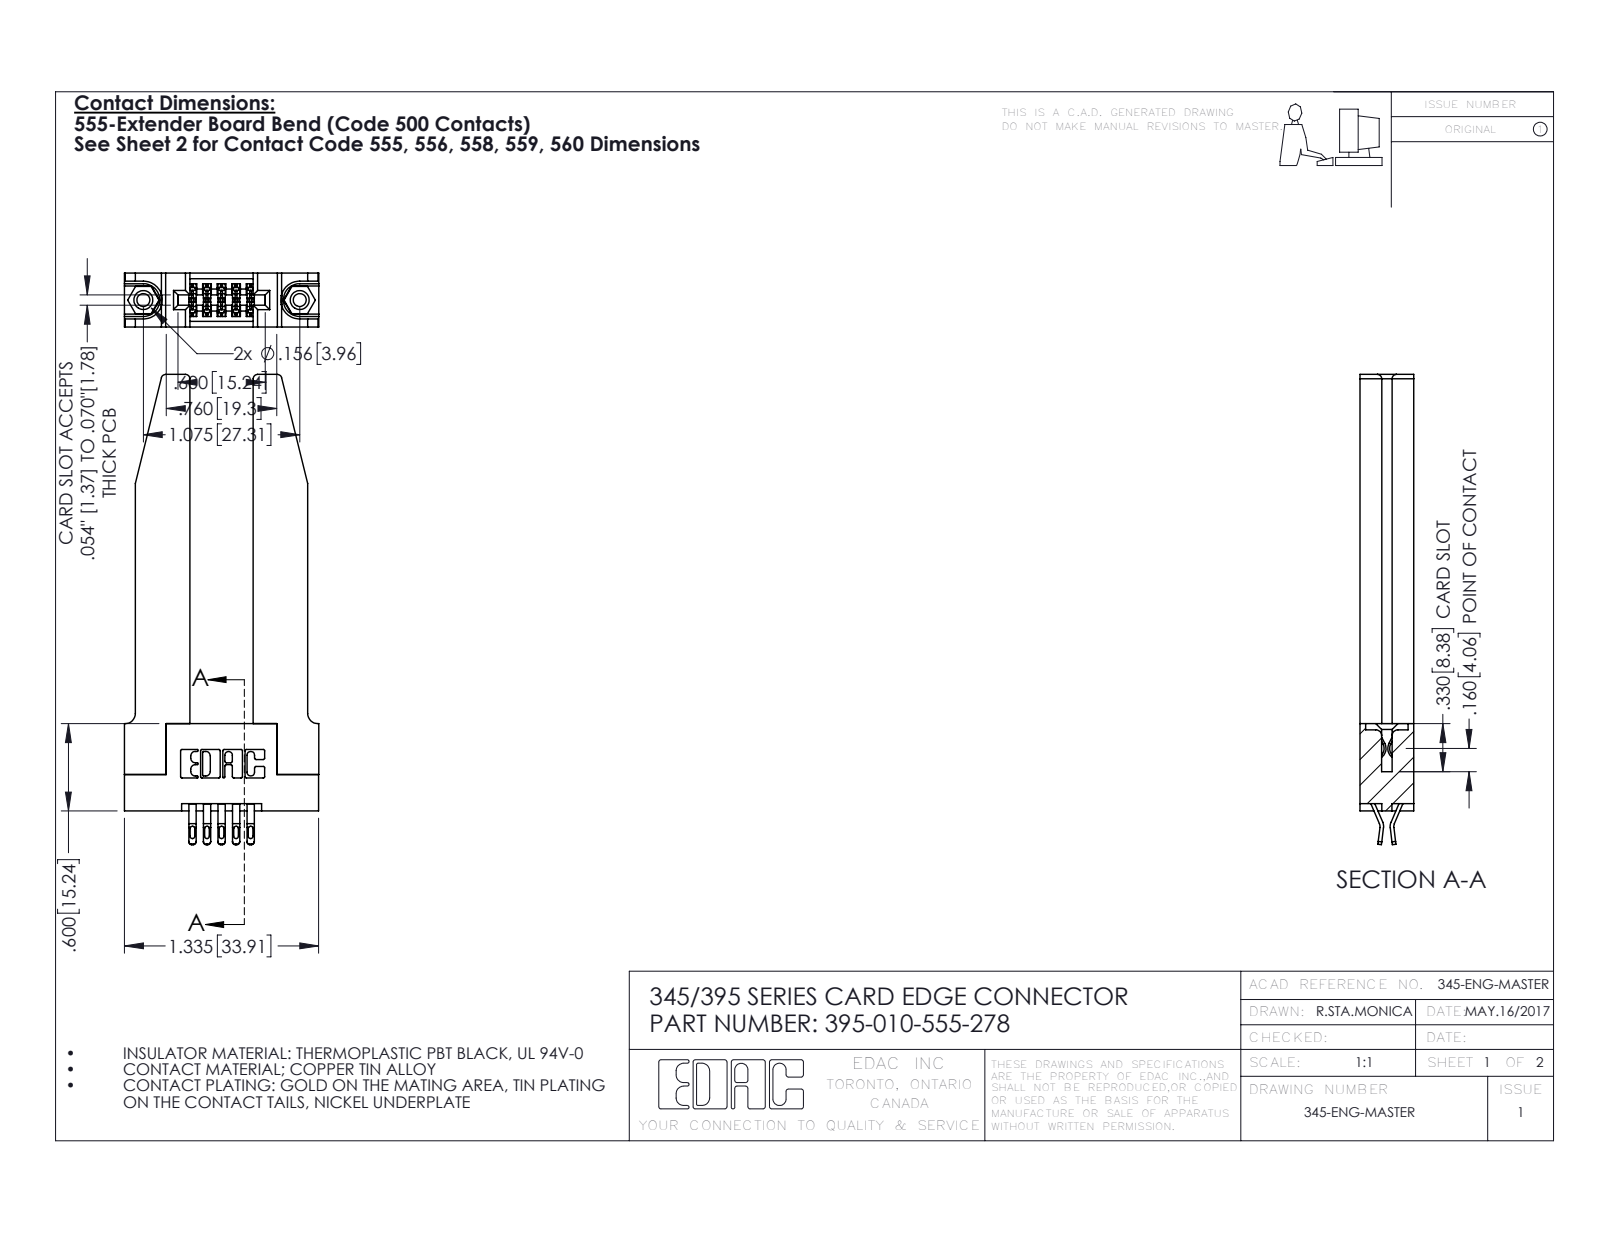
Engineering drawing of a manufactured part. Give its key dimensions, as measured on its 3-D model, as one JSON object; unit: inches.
{"part_name": "345-220-078_345-220-078; 345-250-001_345-250-001-102; 345-292-001_555 Tail; 345 Part_Flush Mounting Lugs - 0.156 Dia-TH (+1 more)", "step_written_by": "SolidWorks 2016 (CONFIG_CONTROL_DESIGN)", "units": "inches", "bodies": {"solids": 15, "faces": 920, "planar": 532, "cylindrical": 336, "other": 52}, "overall_size": [3.232, 1.336, 0.37], "volume_in3": 0.656, "surface_area_in2": 16.48, "round_holes": [[0.089, 2], [0.125, 2], [0.156, 2], [0.064, 1]], "round_bosses_or_shafts": [[0.155, 2]], "partial_cylinders_radius": [[0.016, 25], [0.01, 22], [0.02, 20], [0.006, 15], [0.03, 8], [0.007, 6], [0.031, 6], [0.026, 3]], "face_to_face_distances": [0.37, 0.15, 0.22, 0.435, 0.072, 0.148, 0.077, 0.298, 0.2, 0.095], "hole_center_spacings": [0.27, 0.847, 1.075]}
